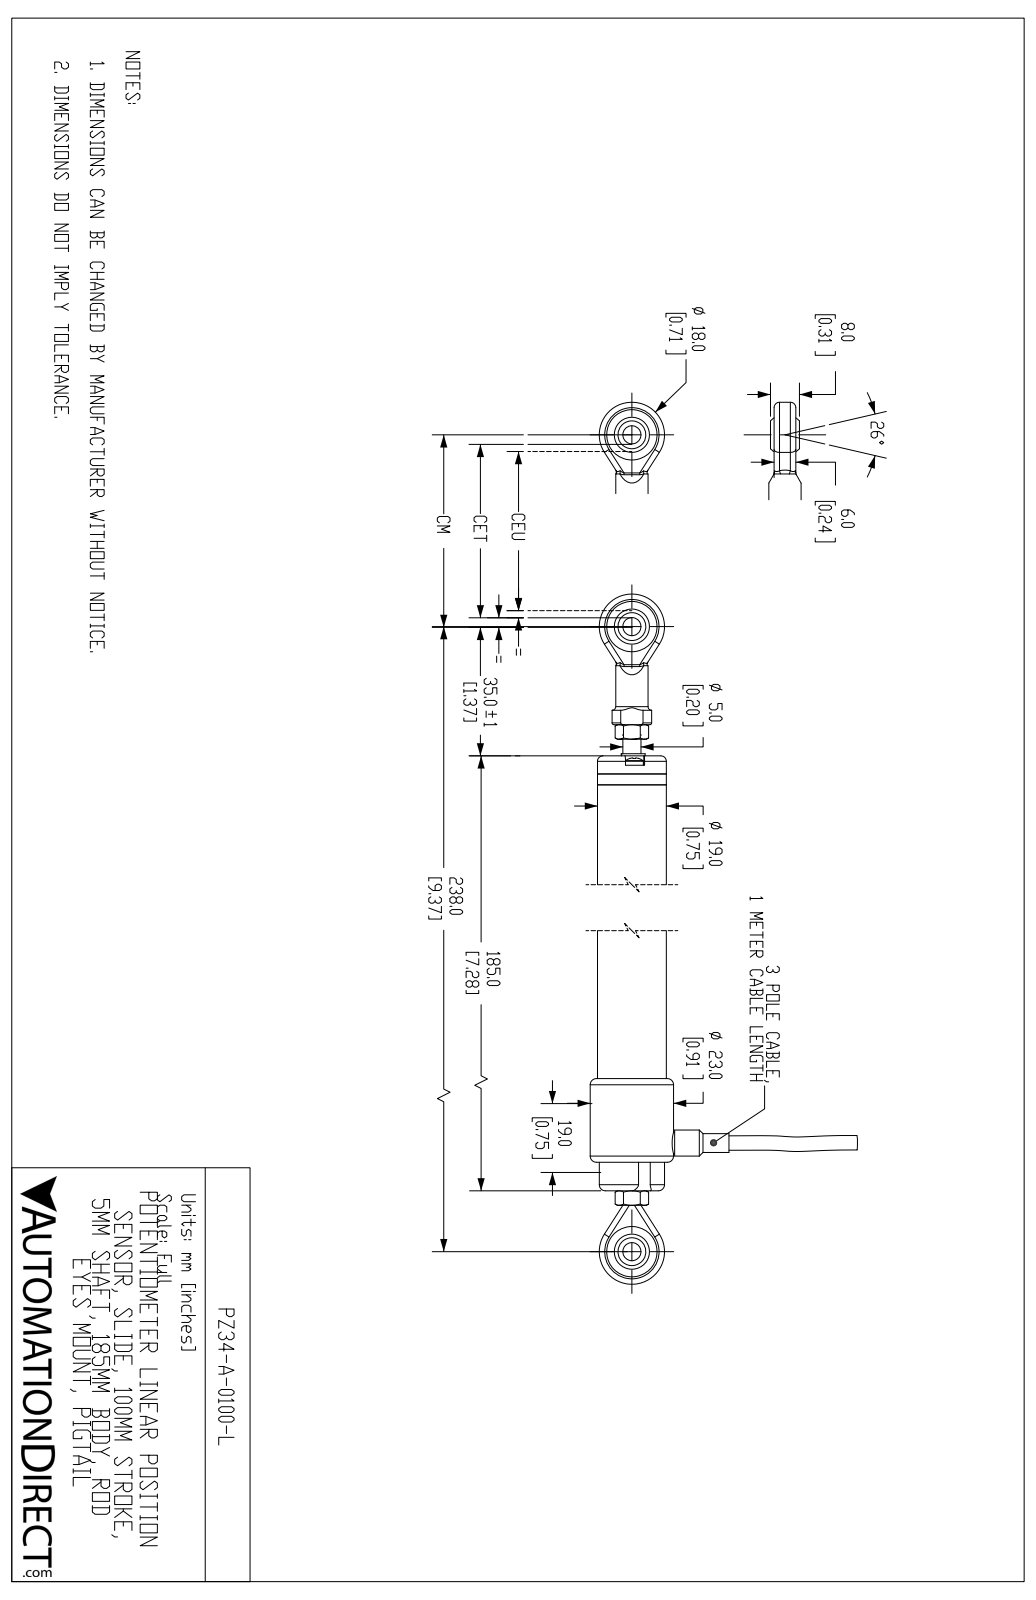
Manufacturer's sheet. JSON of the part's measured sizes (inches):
{"part_name": "PZ34-A-0100-L", "step_written_by": "SolidWorks 2019 (AUTOMOTIVE_DESIGN)", "units": "inches", "bodies": {"solids": 18, "faces": 916, "planar": 334, "cylindrical": 198, "other": 384}, "overall_size": [10.059, 2.904, 0.906], "volume_in3": 3.97, "surface_area_in2": 40.91, "round_holes": [[0.079, 4], [0.114, 4], [0.197, 2], [0.209, 2], [0.547, 2], [0.138, 1], [0.165, 1], [0.24, 1], [0.354, 1], [0.75, 1]], "round_bosses_or_shafts": [[0.197, 5], [0.098, 4], [0.906, 1], [0.748, 1], [0.709, 1], [0.35, 1], [0.283, 1], [0.236, 1]], "partial_cylinders_radius": [[0.059, 8], [0.01, 4], [0.02, 2], [0.039, 2], [0.104, 2], [0.354, 2], [0.017, 1], [0.063, 1]], "face_to_face_distances": [6.378, 6.26, 0.118, 0.315, 0.224, 0.213, 0.217, 0.051, 0.039, 0.264], "hole_center_spacings": [0.269, 0.082, 0.532, 0.539, 9.35]}
